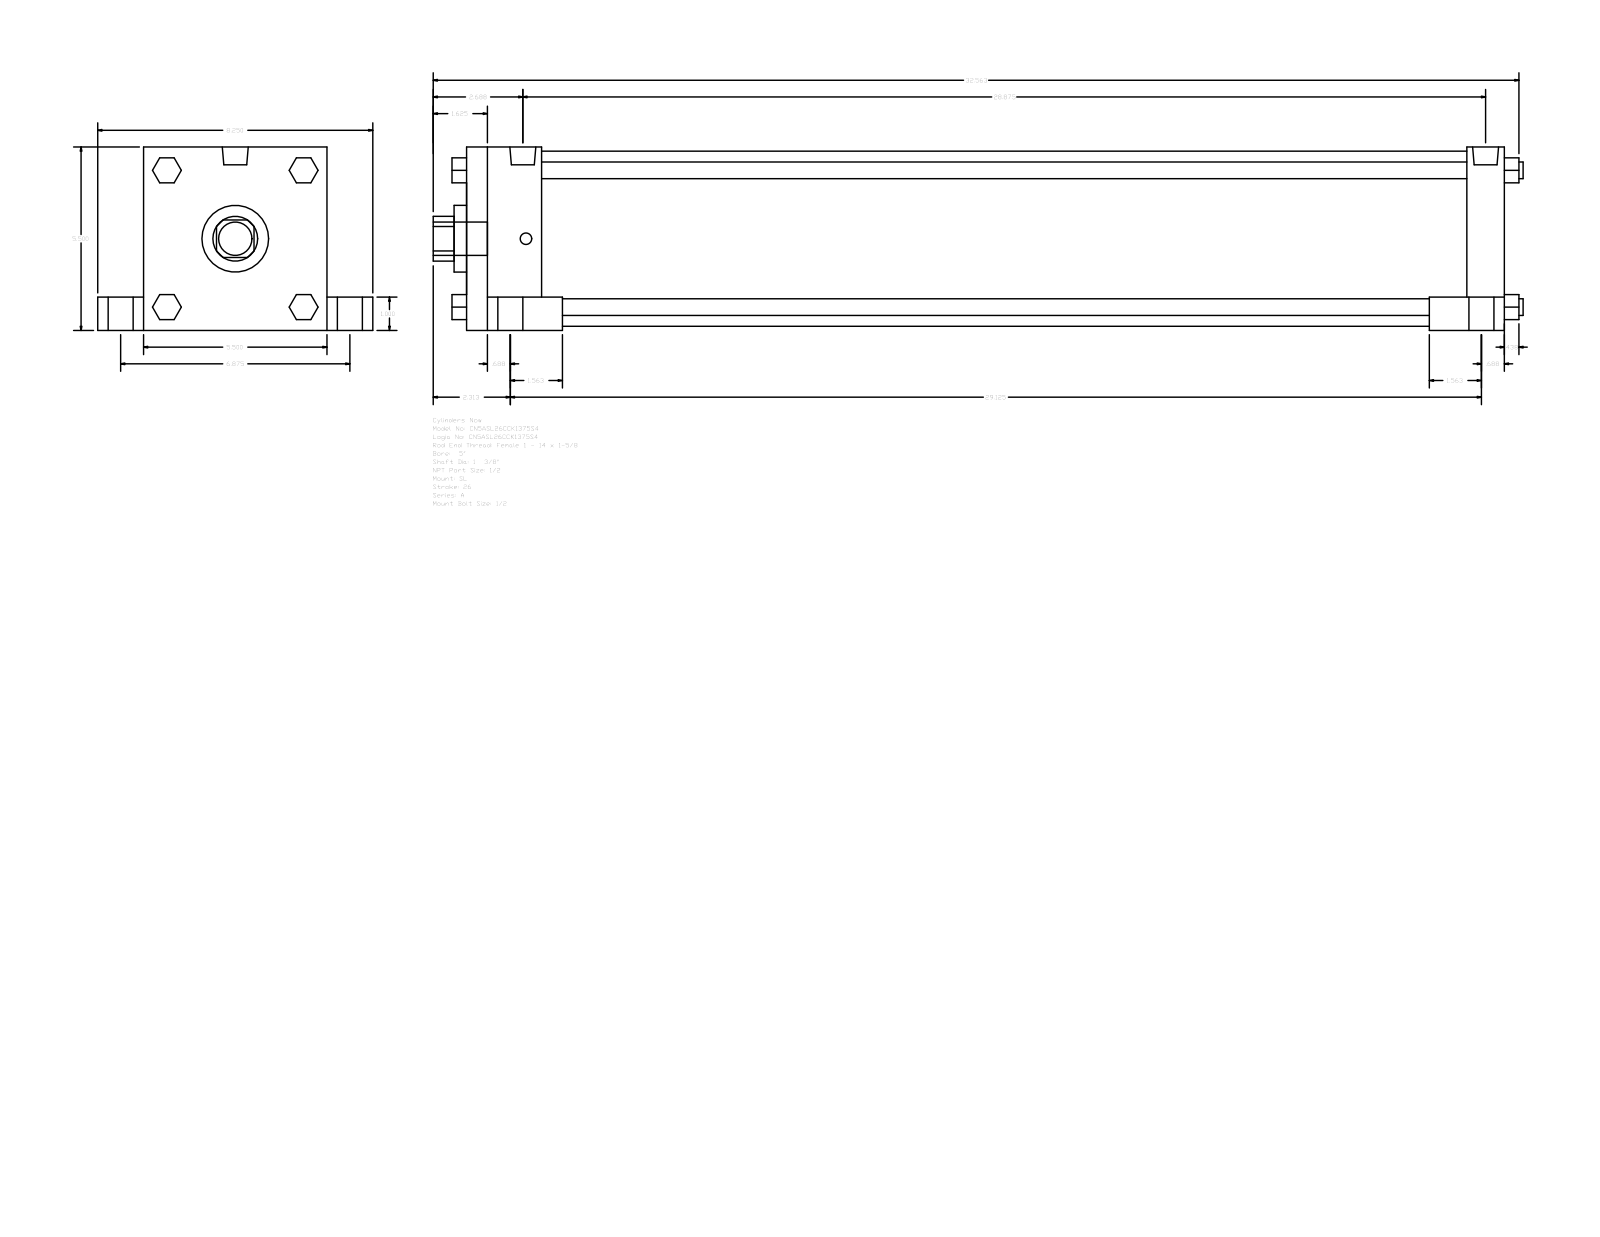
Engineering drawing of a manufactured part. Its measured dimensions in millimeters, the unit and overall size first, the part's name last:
Units: millimetres
Overall size (bounding box): 830.26 × 209.55 × 139.7
Round holes (diameter × count): ⌀34.92 ×1, ⌀50.8 ×1, ⌀133.35 ×1
Round bosses / shafts (diameter × count): ⌀25.4 ×5, ⌀19.05 ×4, ⌀12.7 ×4, ⌀8.73 ×4, ⌀19.77 ×2
Partial cylindrical surfaces — rounded edges, fillets, slot ends (radius × count): R17.06 ×1
Main face-to-face distances: 139.7, 790.58, 57.15, 733.43, 25.4, 114.3, 34.93, 174.63, 28.58, 762
Bodies: 0 solids, 150 faces (114 planar, 36 cylindrical, 0 other)
Part name (STEP PRODUCT): A_SL__0500_1.375
STEP written by: GSSL Pune (CONFIG_CONTROL_DESIGN)
